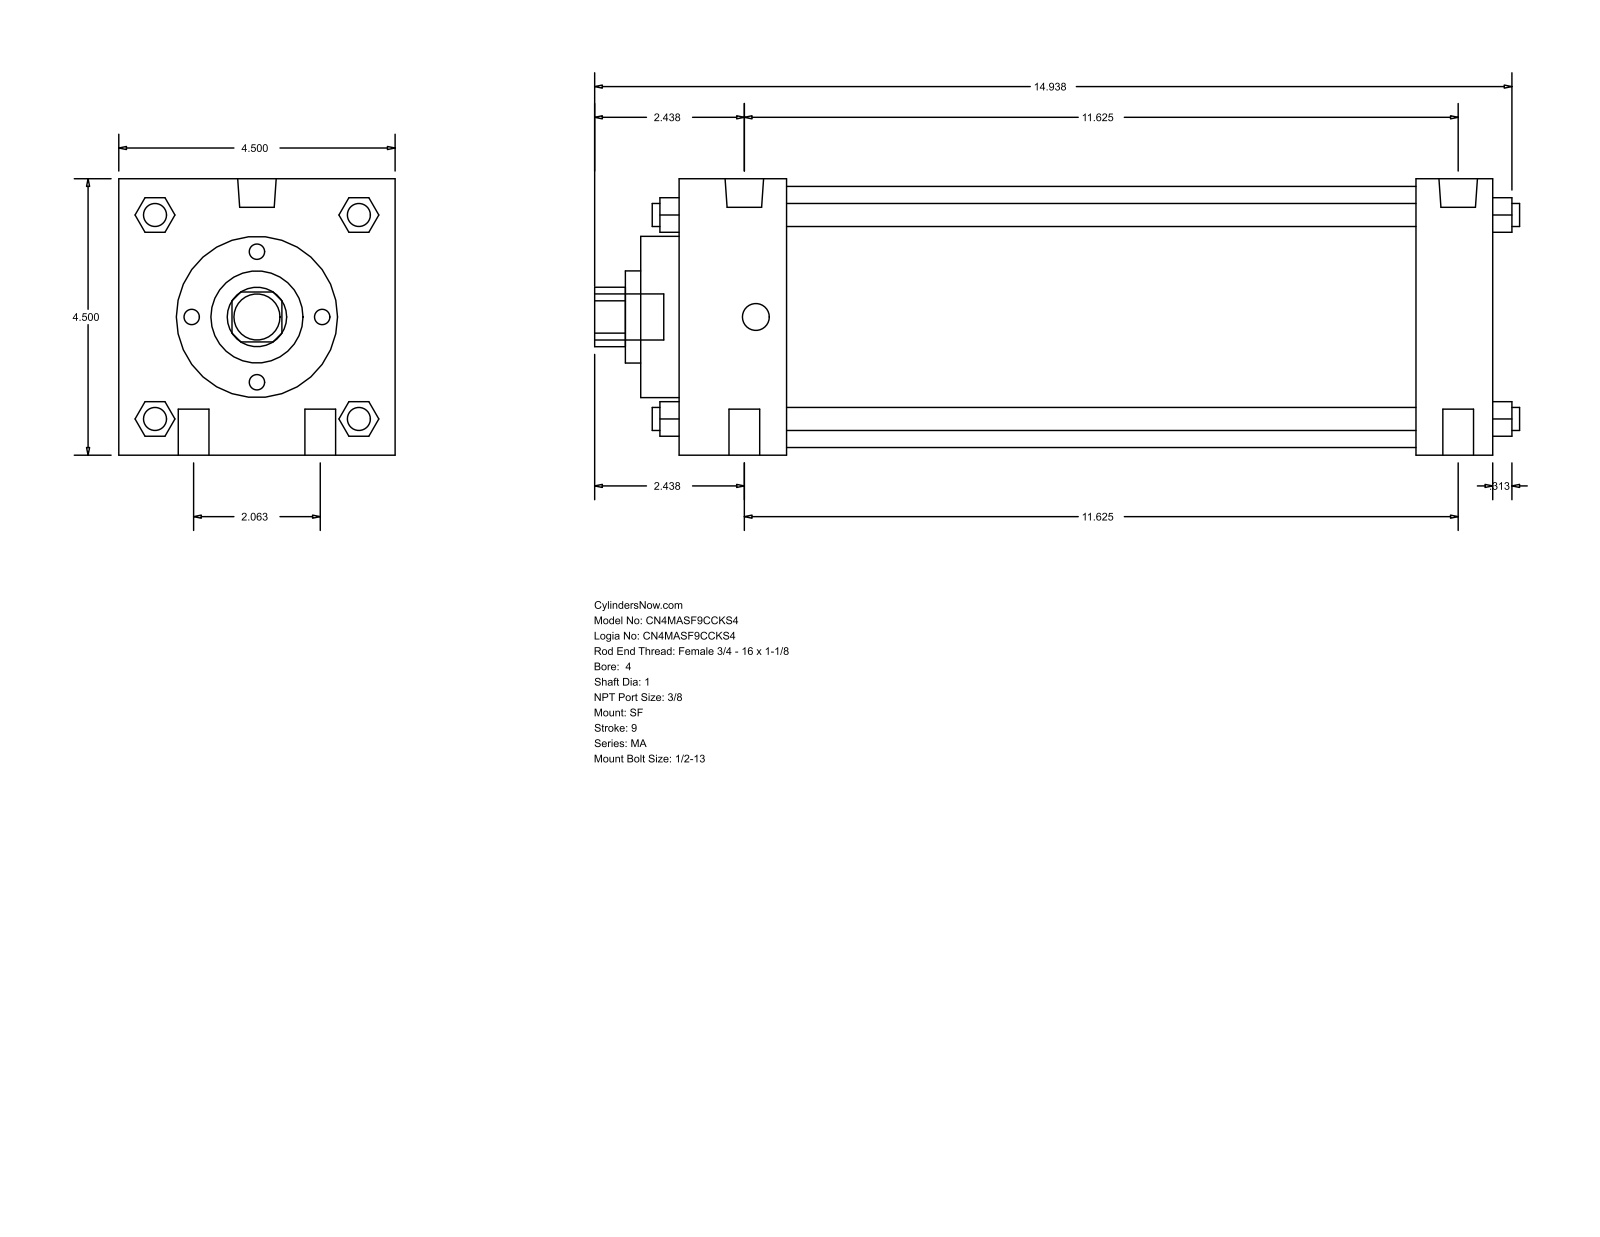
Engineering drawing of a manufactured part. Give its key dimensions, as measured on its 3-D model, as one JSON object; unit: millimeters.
{"part_name": "MA_SF__0400_1", "step_written_by": "GSSL Pune (CONFIG_CONTROL_DESIGN)", "units": "millimeters", "bodies": {"solids": 0, "faces": 126, "planar": 95, "cylindrical": 31, "other": 0}, "overall_size": [382.59, 114.3, 114.3], "round_holes": [[25.4, 1], [38.1, 1], [66.67, 1], [107.95, 1]], "round_bosses_or_shafts": [[12.7, 4], [9.53, 4], [15.93, 2], [11.11, 2], [19.05, 1]], "partial_cylinders_radius": [[12.29, 1]], "face_to_face_distances": [114.3, 336.56, 304.81, 31.75, 44.46, 260.35, 292.1, 15.87, 60.33, 320.68]}
